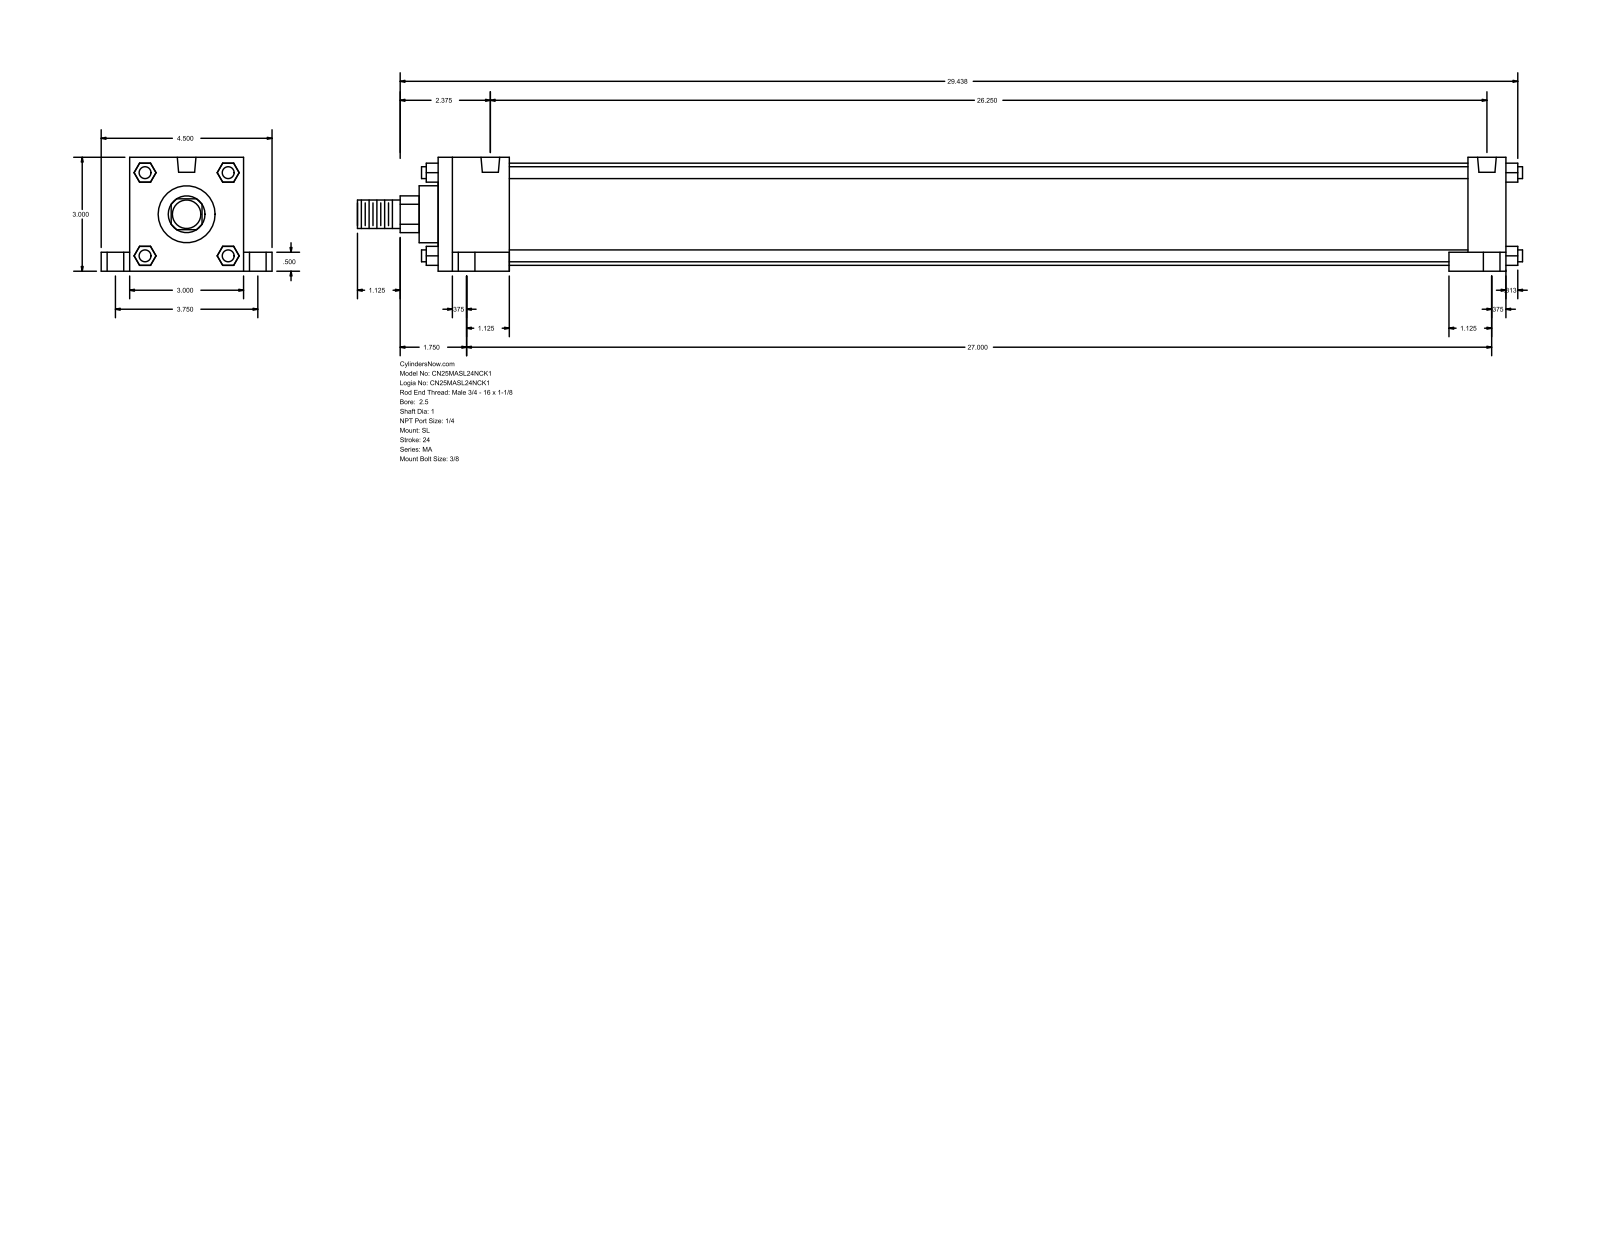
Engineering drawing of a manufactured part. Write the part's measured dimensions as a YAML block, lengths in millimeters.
part_name: "MA_SL__0250_1"
step_written_by: "GSSL Pune (CONFIG_CONTROL_DESIGN)"
units: millimeters
bodies: {solids: 0, faces: 148, planar: 112, cylindrical: 36, other: 0}
overall_size: [779.46, 114.3, 76.2]
round_holes:
  - {diameter: 7.94, count: 4}
  - {diameter: 11.11, count: 4}
  - {diameter: 17.46, count: 4}
  - {diameter: 12.49, count: 2}
round_bosses_or_shafts:
  - {diameter: 7.94, count: 4}
  - {diameter: 68.33, count: 1}
  - {diameter: 38.1, count: 1}
  - {diameter: 25.4, count: 1}
  - {diameter: 19.05, count: 1}
partial_cylinders:
  - {radius: 12.29, count: 1}
face_to_face_distances: [76.2, 714.37, 12.7, 641.35, 25.39, 47.63, 666.74, 688.98, 19.05, 95.25]
hole_center_spacings: [47.73, 50.2, 95.24, 666.75, 671.61, 684.29, 685.8, 692.38]
